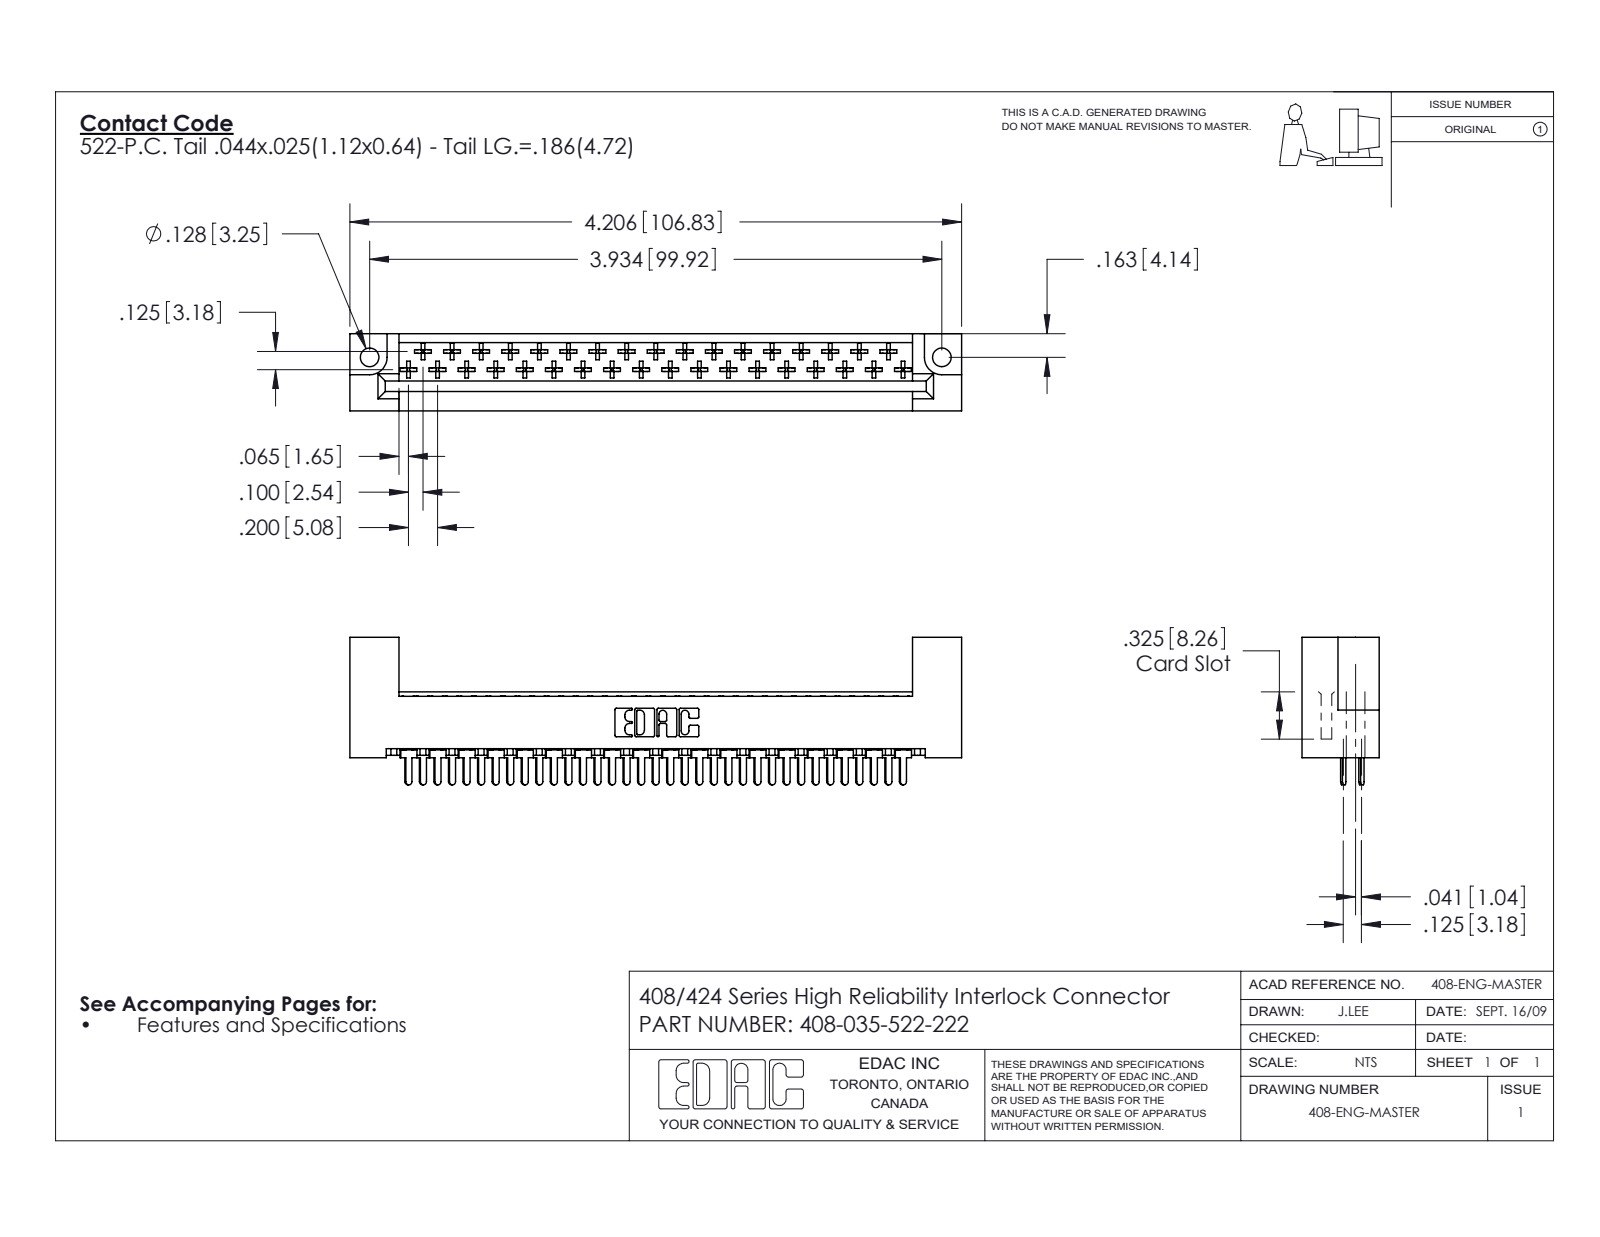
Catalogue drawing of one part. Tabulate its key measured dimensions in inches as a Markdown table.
| quantity | value |
| --- | --- |
| part name | 408-035-522-222; 408 Part_035 - 2; 408-290-001_408-290-122 |
| STEP written by | SolidWorks 2016 (CONFIG_CONTROL_DESIGN) |
| units | inches |
| bodies | 36 solids, 2064 faces (1559 planar, 365 cylindrical, 140 other) |
| overall size | 4.206 × 1.014 × 0.531 |
| volume | 0.815 in³ |
| surface area | 24.02 in² |
| round holes (diameter × count) | 0.128 × 2 |
| partial cylindrical surfaces (radius × count) | 0.01 × 210, 0.02 × 37, 0.022 × 35, 0.01 × 22, 0.007 × 6, 0.031 × 6, 0.026 × 3, 0.12 × 2 |
| main face-to-face distances | 0.531, 0.125, 0.1, 0.025, 0.025, 0.361, 0.235, 0.259, 0.398, 0.217 |
| hole center spacings | 3.934 |
